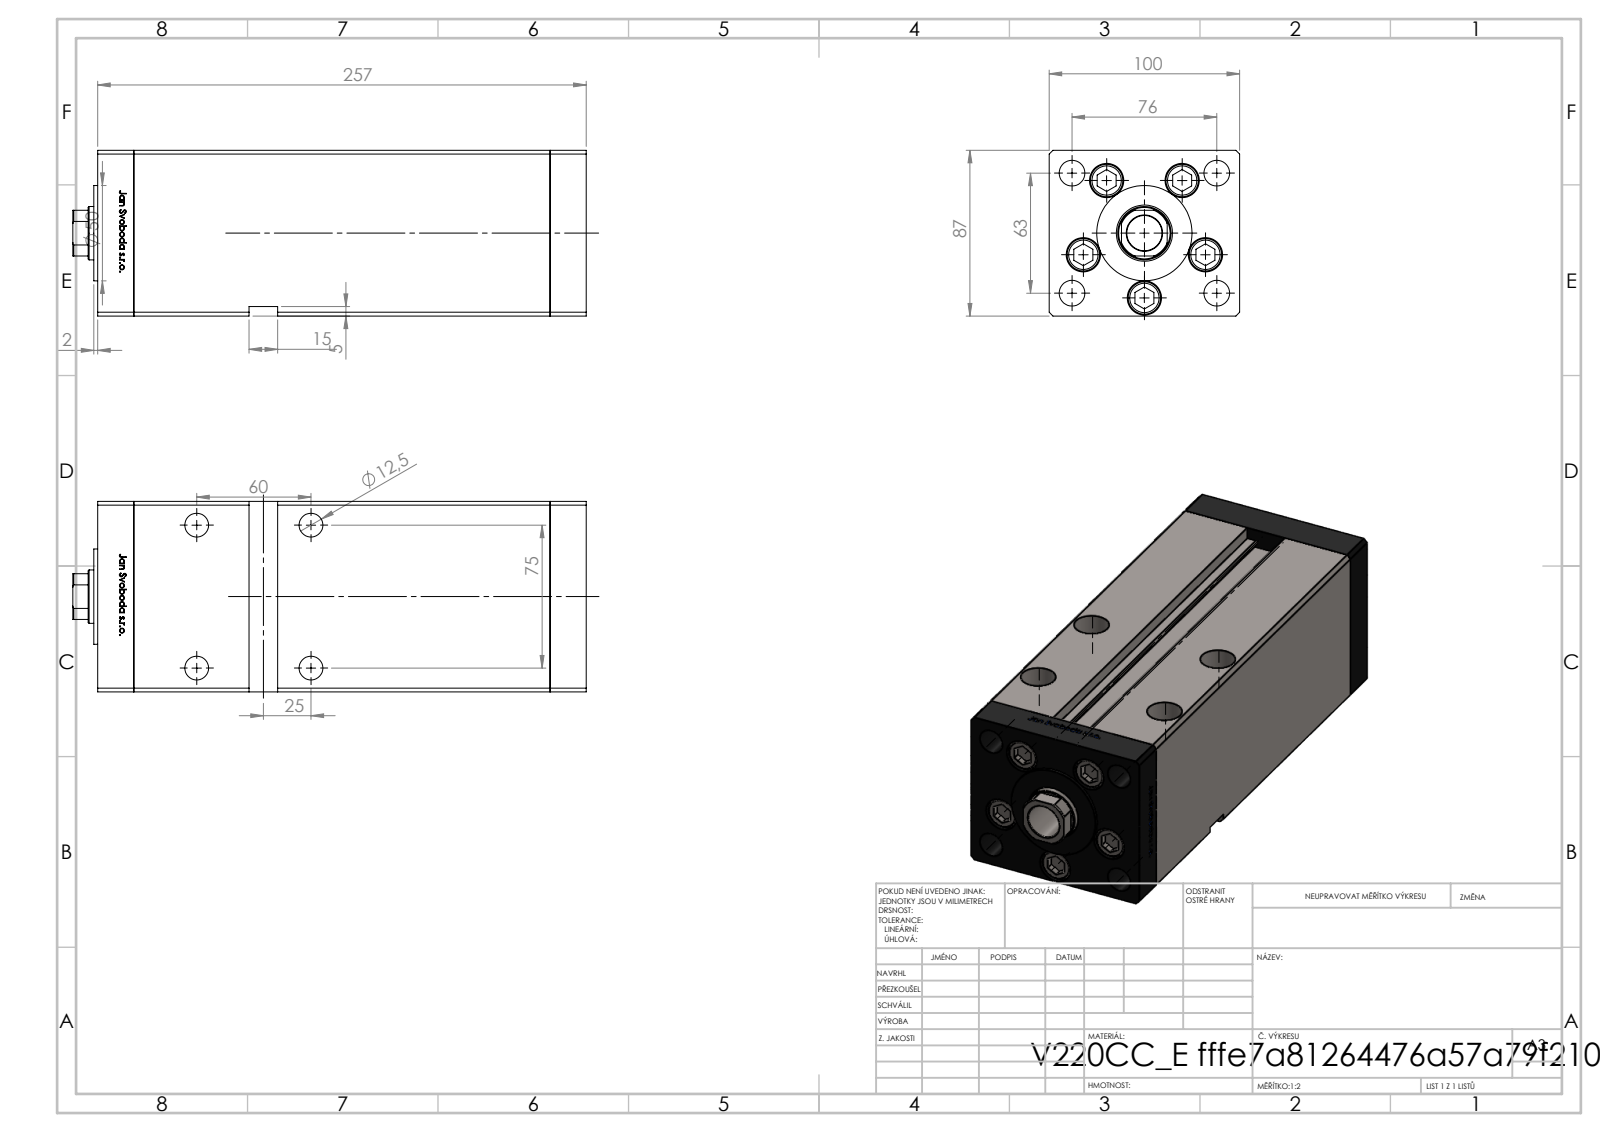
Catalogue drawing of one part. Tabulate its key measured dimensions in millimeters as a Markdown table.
| quantity | value |
| --- | --- |
| part name | V220C BACK_E; V220C_E MIDDLE; V220C_FRONT_E; ALLEN BOLT (+1 more) |
| STEP written by | SolidWorks 2019 (CONFIG_CONTROL_DESIGN) |
| units | millimeters |
| bodies | 14 solids, 1212 faces (473 planar, 165 cylindrical, 574 other) |
| overall size | 269.5 × 100 × 87 |
| volume | 1 865 000 mm³ |
| surface area | 265 784 mm² |
| round holes (diameter × count) | 13.5 × 11, 18 × 5, 18.5 × 5, 12.5 × 4, 2 × 2, 13.16 × 2, 28 × 1, 29.5 × 1 |
| round bosses / shafts (diameter × count) | 17 × 5, 8 × 5, 50 × 1 |
| partial cylindrical surfaces (radius × count) | 0.93 × 2, 13.5 × 1 |
| main face-to-face distances | 100, 87, 19, 218.5, 237.5, 34.25, 256.5, 15.25, 203.25, 222.25 |
| hole center spacings | 34, 18.59, 39.64, 49.36, 57.95, 21.03, 38.08, 39.27 |
